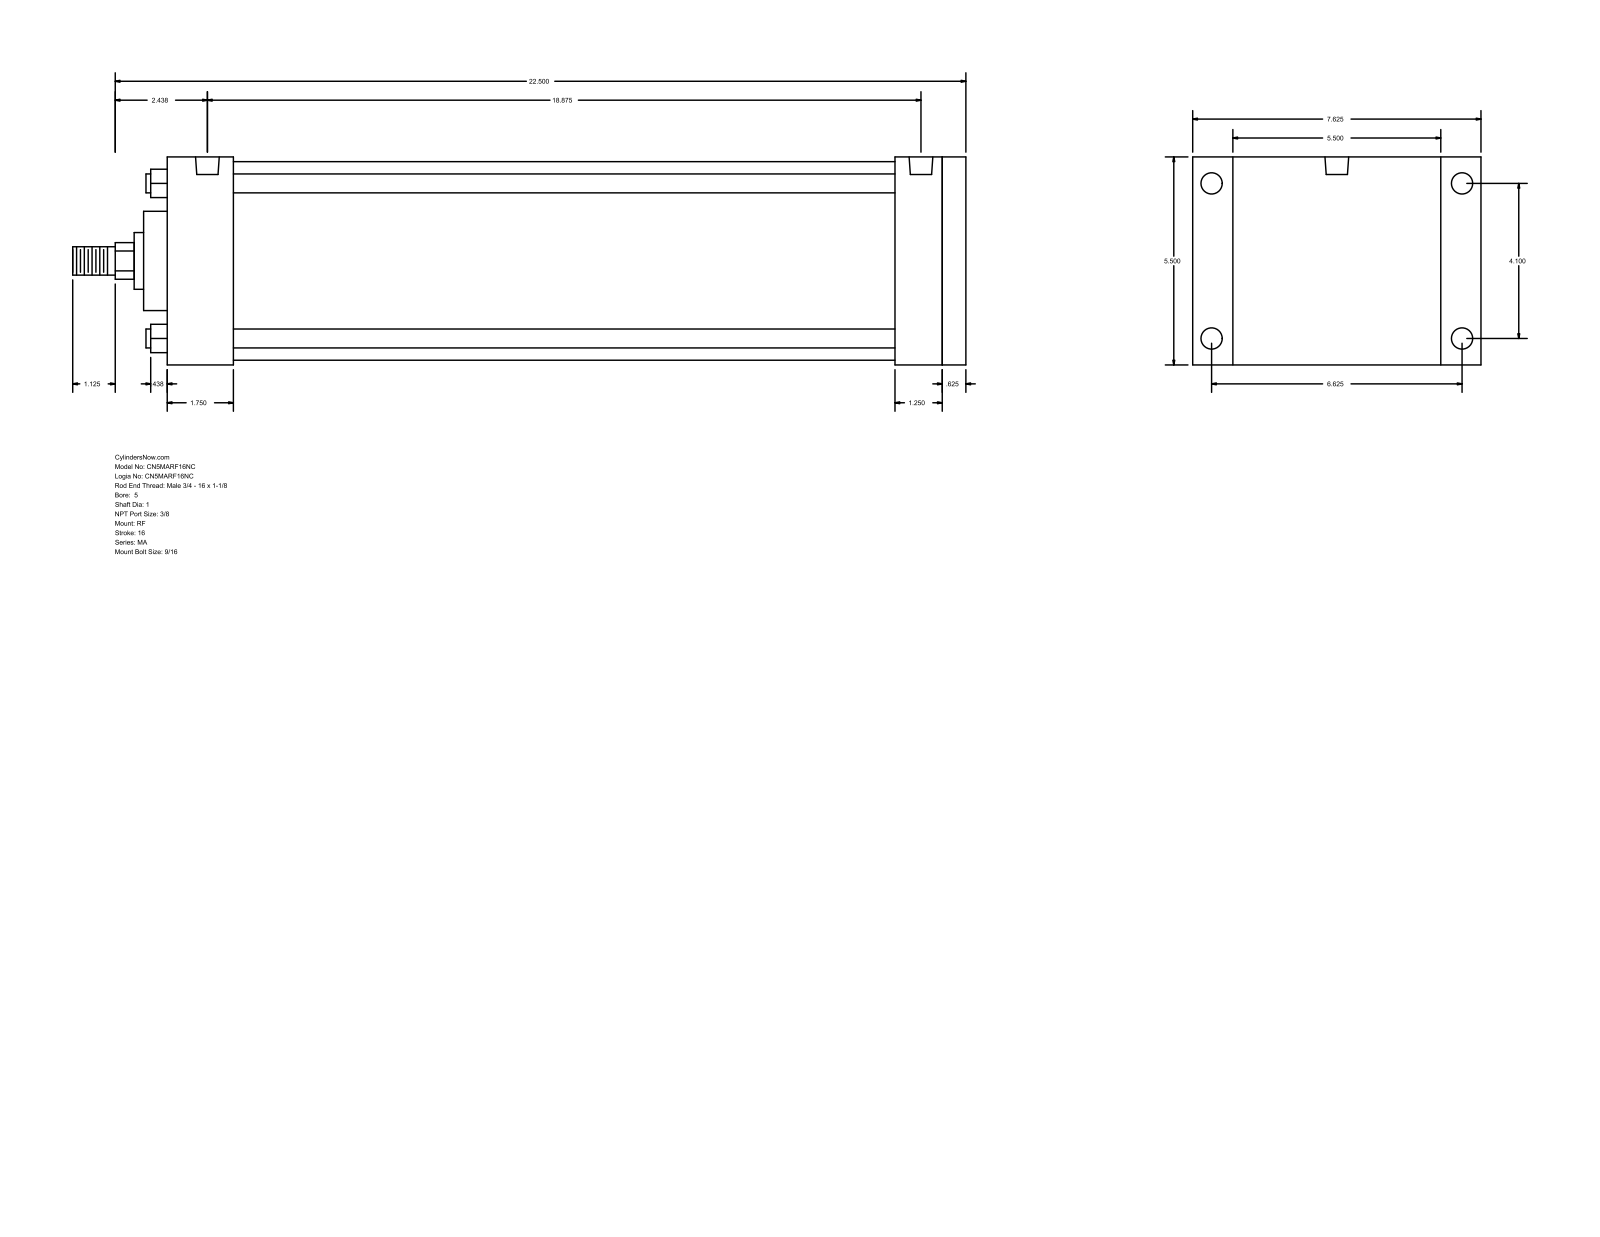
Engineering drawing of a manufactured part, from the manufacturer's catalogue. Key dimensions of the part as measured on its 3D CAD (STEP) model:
Part name (STEP PRODUCT): MA_RF__0500_1
STEP written by: GSSL Pune (CONFIG_CONTROL_DESIGN)
Units: millimetres
Bodies: 0 solids, 94 faces (65 planar, 29 cylindrical, 0 other)
Overall size (bounding box): 600.08 × 193.68 × 139.7
Round holes (diameter × count): ⌀11.11 ×4, ⌀14.29 ×4, ⌀15.93 ×2
Round bosses / shafts (diameter × count): ⌀12.7 ×4, ⌀133.35 ×1, ⌀66.67 ×1, ⌀38.1 ×1, ⌀25.4 ×1, ⌀19.05 ×1
Partial cylindrical surfaces — rounded edges, fillets, slot ends (radius × count): R12.29 ×1
Main face-to-face distances: 139.7, 536.58, 520.7, 15.88, 47.62, 44.46, 476.24, 492.12, 488.96, 444.5
Hole centre spacings: 4.76, 104.14, 168.28, 197.9, 469.91, 474.67, 479.43
